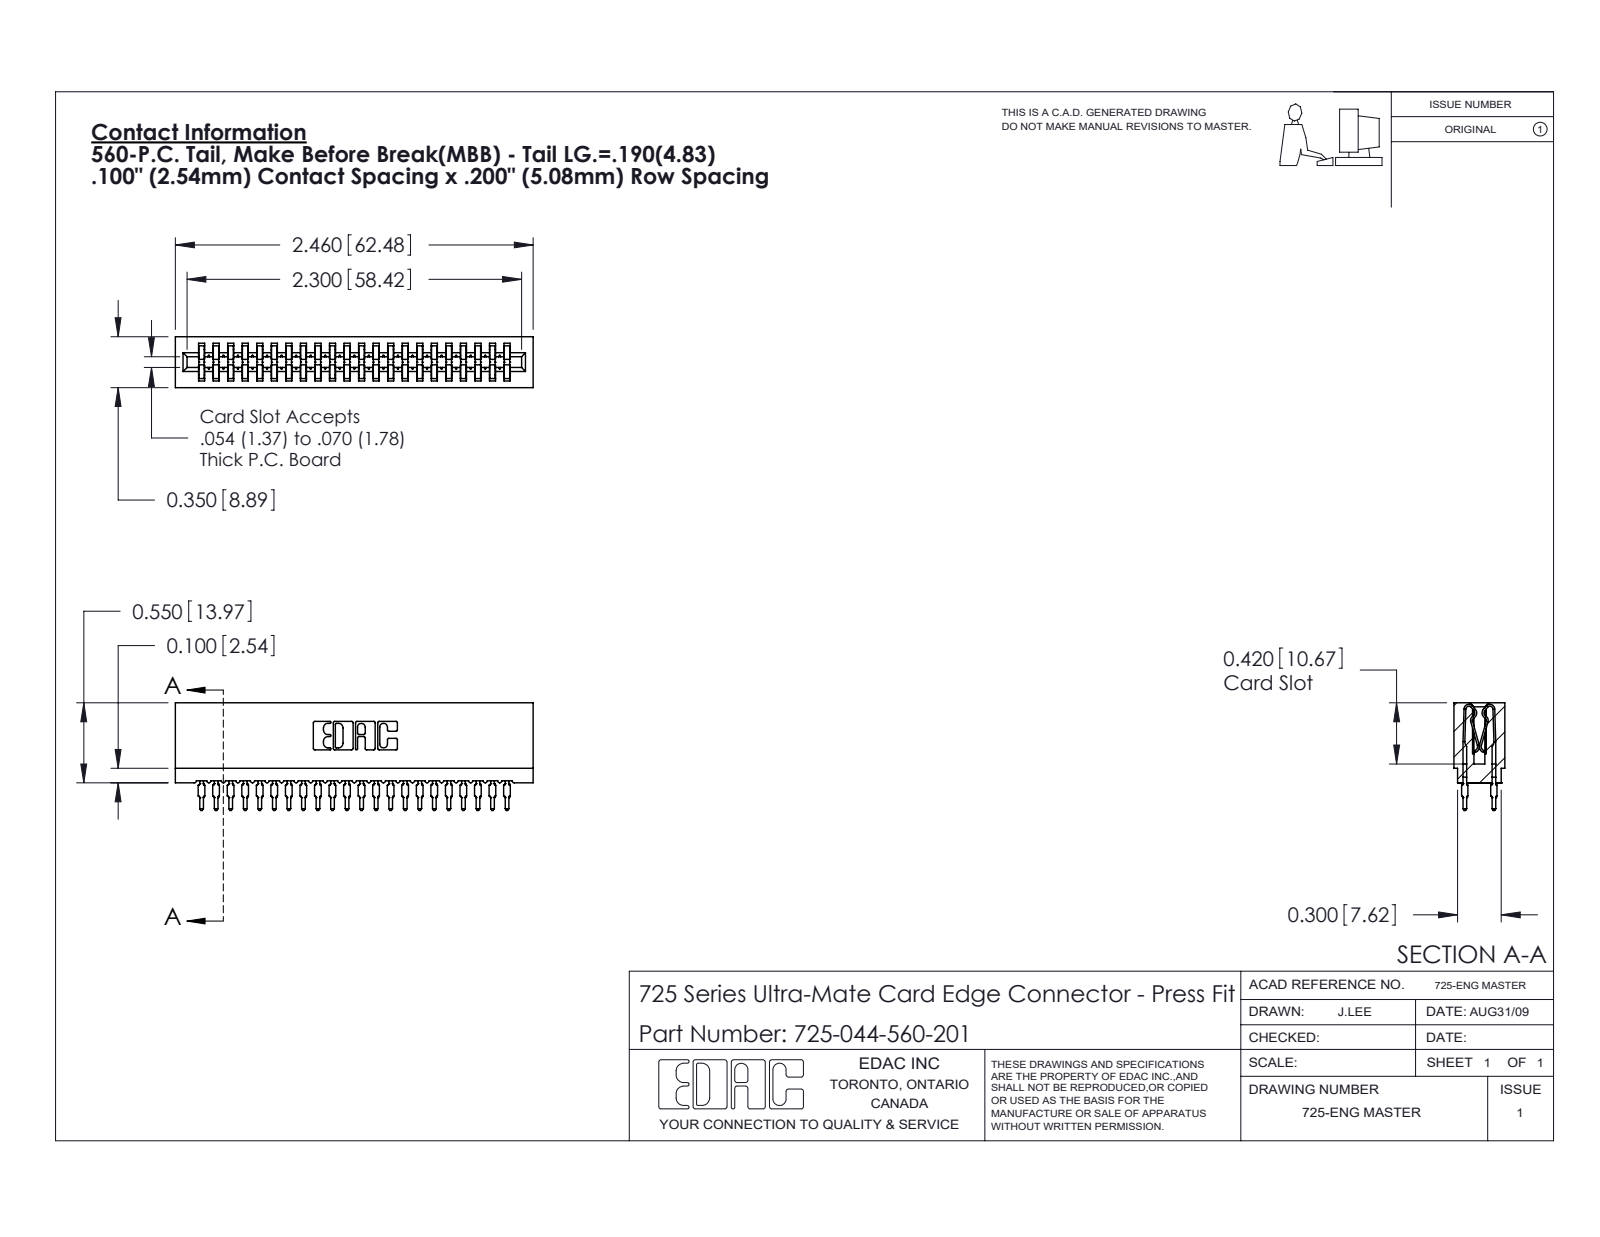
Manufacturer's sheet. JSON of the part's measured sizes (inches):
{"part_name": "725-044-560-201; 725 Part_Insulator Option - 01; 745-292-001_560", "step_written_by": "SolidWorks 2020 (CONFIG_CONTROL_DESIGN)", "units": "inches", "bodies": {"solids": 45, "faces": 4429, "planar": 2299, "cylindrical": 986, "other": 1144}, "overall_size": [2.46, 0.741, 0.35], "volume_in3": 0.318, "surface_area_in2": 17.5, "partial_cylinders_radius": [[0.021, 88], [0.015, 44], [0.01, 22], [0.005, 8], [0.011, 8], [0.007, 6], [0.031, 6], [0.026, 3]], "face_to_face_distances": [0.2, 0.1, 0.3, 0.35, 0.063, 0.287, 0.6, 0.4, 0.7, 0.5]}
